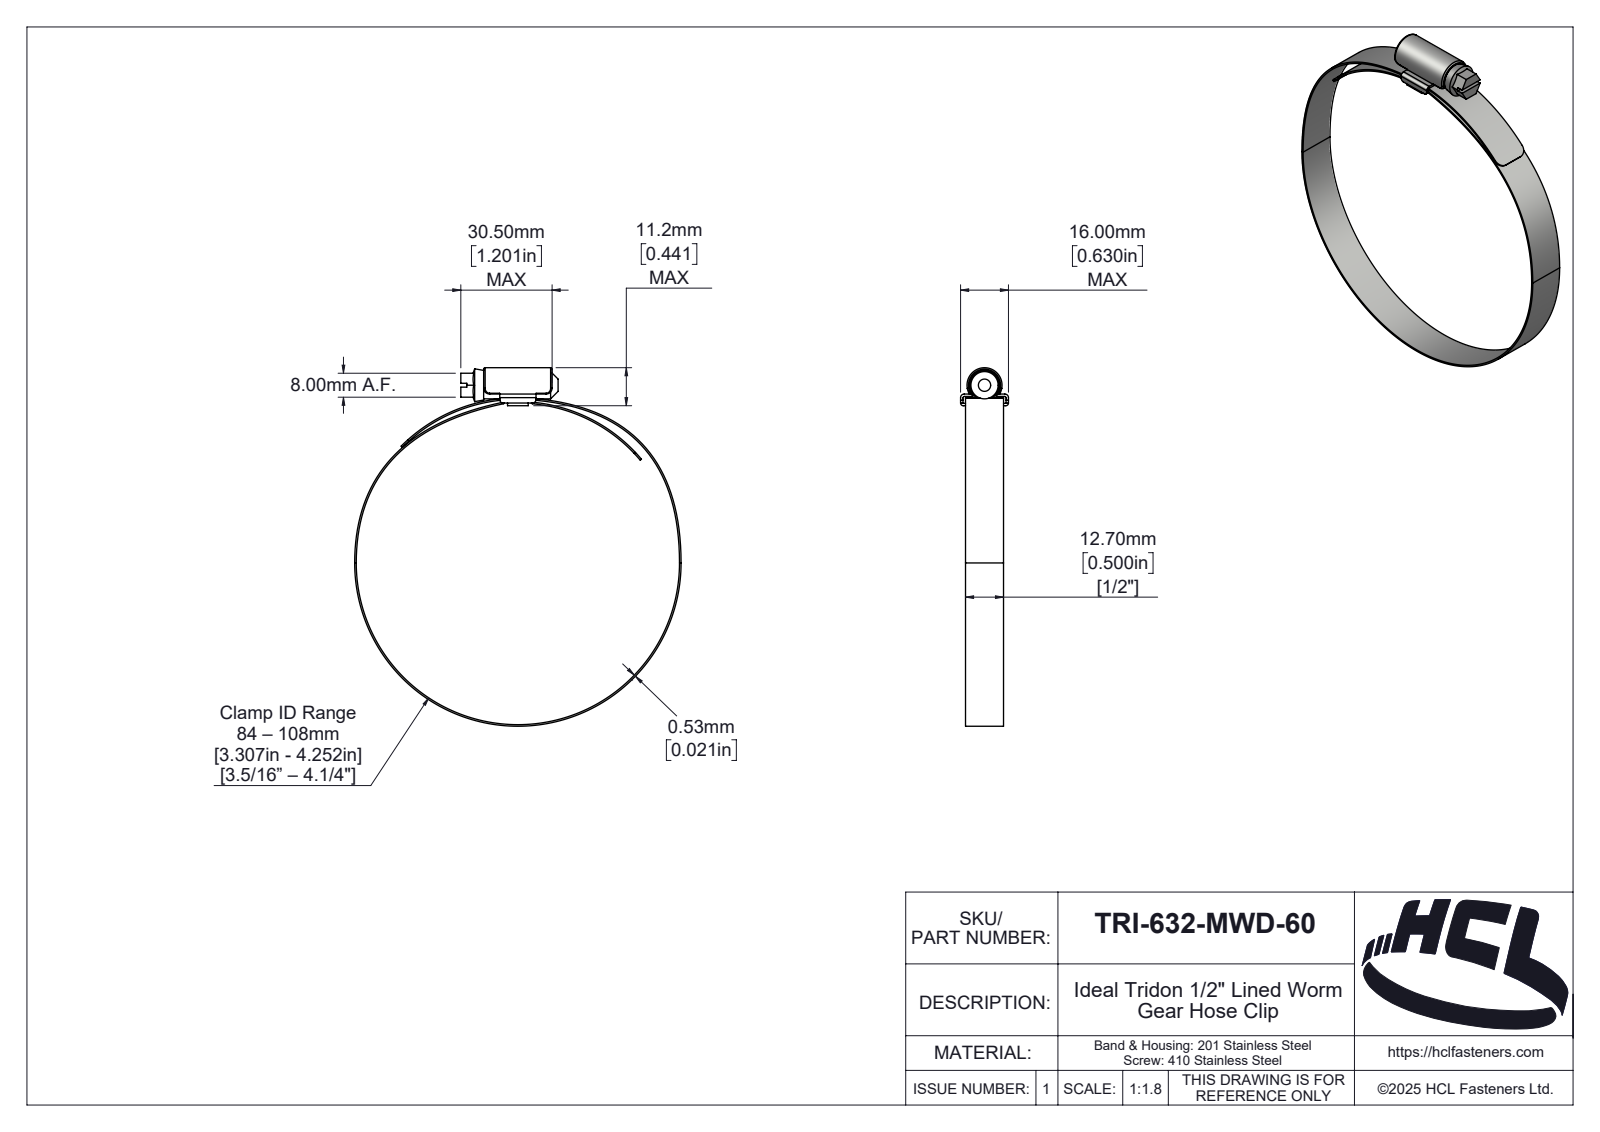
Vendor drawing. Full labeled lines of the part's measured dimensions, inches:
Part name (STEP PRODUCT): TRI-632-MWD-60
STEP written by: SolidWorks 2025 (AUTOMOTIVE_DESIGN)
Units: inches
Bodies: 3 solids, 217 faces (49 planar, 99 cylindrical, 69 other)
Overall size (bounding box): 4.714 × 4.294 × 0.63
Volume: 0.34 in³ · Surface area: 22.02 in²
Round bosses / shafts (diameter × count): ⌀0.358 ×1
Partial cylindrical surfaces — rounded edges, fillets, slot ends (radius × count): R0.02 ×10, R0.118 ×4, R0.004 ×2, R0.035 ×2, R0.039 ×2, R0.041 ×2, R0.047 ×2, R0.079 ×2
Main face-to-face distances: 0.5, 0.031, 0.122, 0.091, 0.154, 0.065, 0.565, 0.598, 0.033, 0.533
